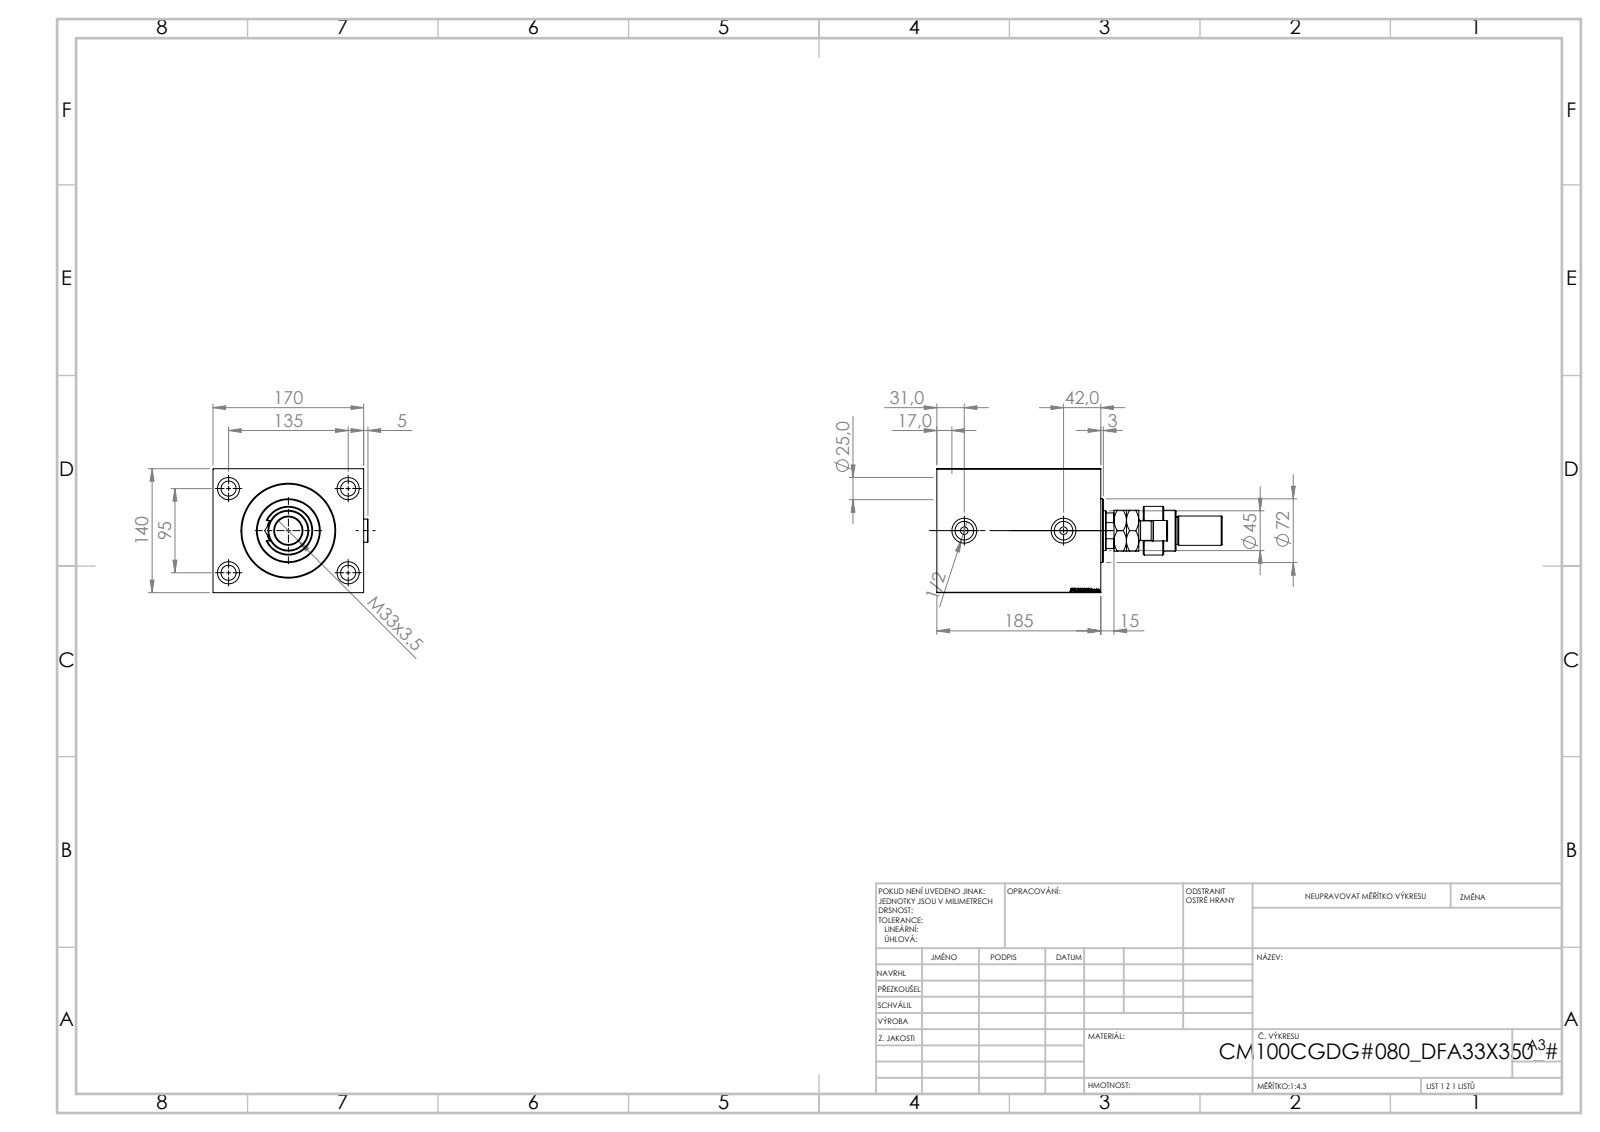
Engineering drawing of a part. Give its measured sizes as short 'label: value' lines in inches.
name: V450CM_C_Body; FEMALE_PART_FOR_DFA; V450CM_VC_B; Zatka_OIL_PORT (+2 more)
written by: SolidWorks 2019 (CONFIG_CONTROL_DESIGN)
unit: in
bodies: 7 solids, 1004 faces (471 planar, 91 cylindrical, 442 other)
size: 12.677 × 6.886 × 5.512
volume: 234.3 in³; area: 573 in²
holes: 4× ⌀0.669, 4× ⌀0.984, 2× ⌀0.335, 2× ⌀0.825, 2× ⌀1.102, 1× ⌀1.24, 1× ⌀1.535, 1× ⌀1.772, 1× ⌀1.909, 1× ⌀3.937, 1× ⌀4.016, 1× ⌀4.134
bosses: 2× ⌀1.024, 1× ⌀2.835, 1× ⌀2.165, 1× ⌀1.811, 1× ⌀1.378, 1× ⌀1.299, 1× ⌀1.22, 1× ⌀0.866
rounds: 1× R0.453, 1× R0.866
face distances: 6.693, 5.512, 7.283, 1.024, 6.26, 3.543, 0.591, 3.15, 2.52, 5.669
hole spacings: 3.25, 3.74, 5.315, 6.499, 4.409
